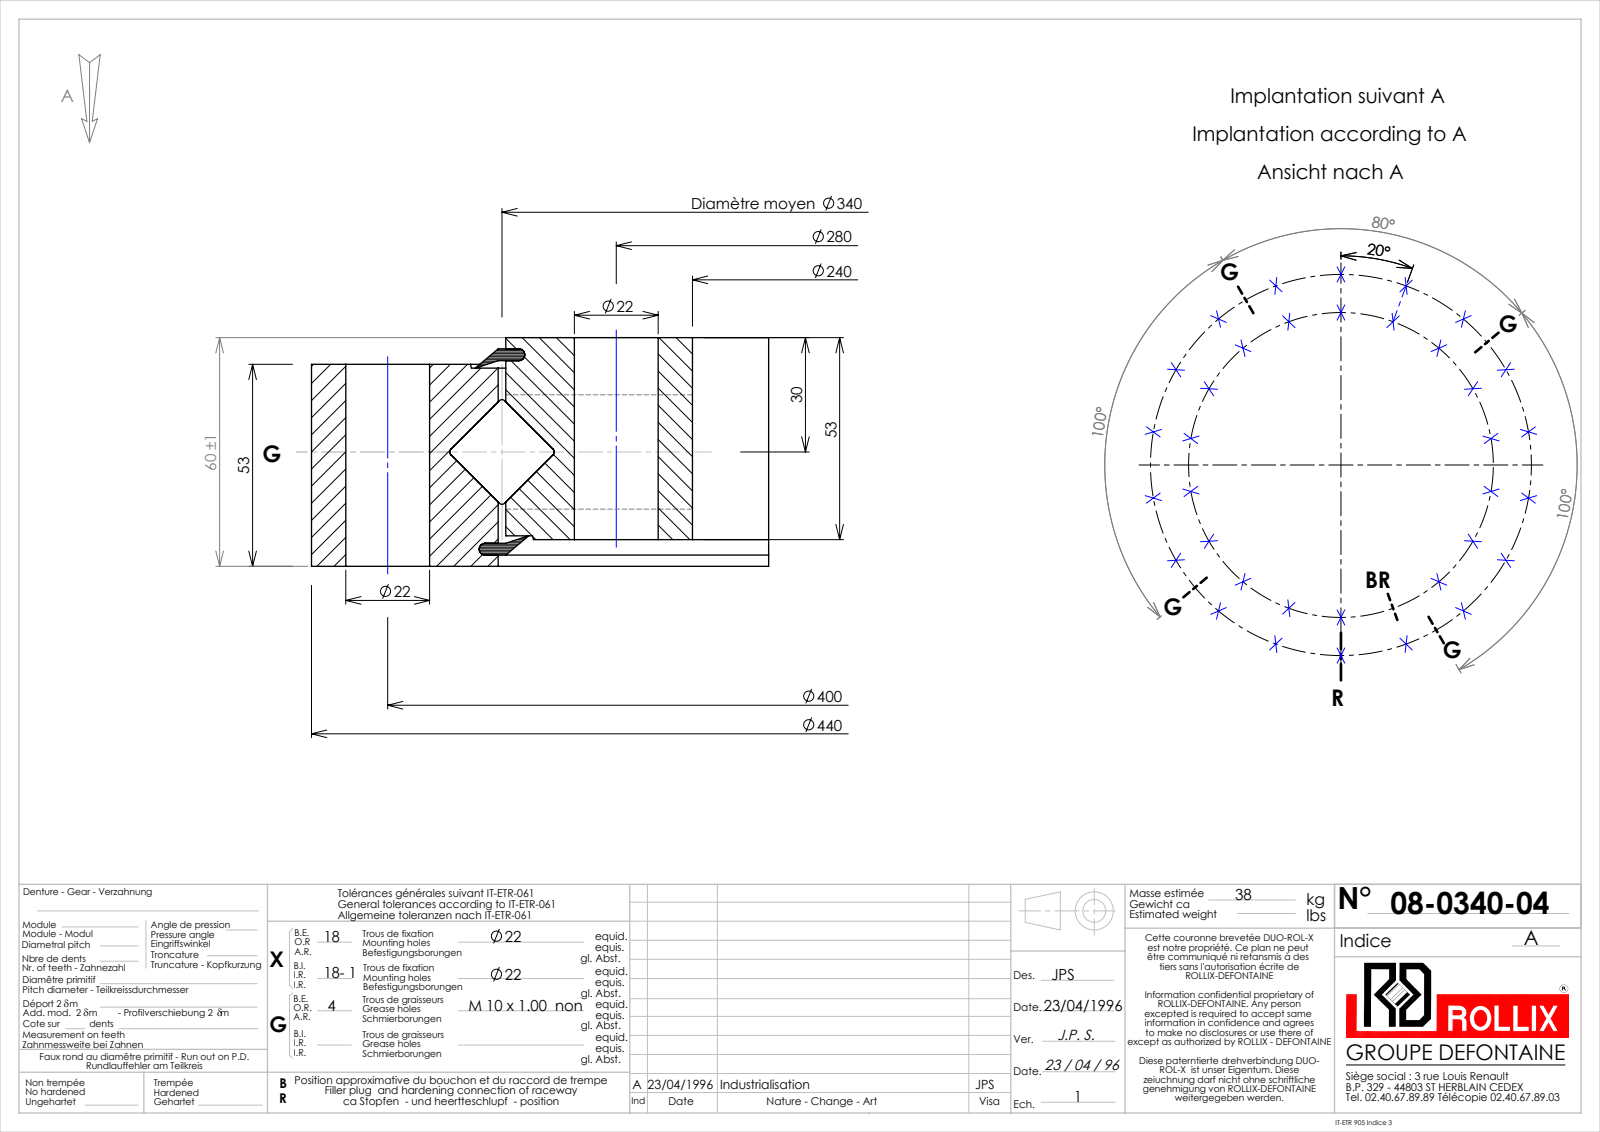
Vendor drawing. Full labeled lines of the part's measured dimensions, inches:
Part name (STEP PRODUCT): 08-0340-04
STEP written by: SolidWorks 2016 (CONFIG_CONTROL_DESIGN)
Units: inches
Bodies: 5 solids, 157 faces (16 planar, 96 cylindrical, 45 other)
Overall size (bounding box): 17.323 × 17.323 × 2.362
Volume: 273.9 in³ · Surface area: 1 003 in²
Round holes (diameter × count): ⌀0.866 ×35, ⌀0.354 ×4, ⌀9.449 ×1, ⌀13.465 ×1
Round bosses / shafts (diameter × count): ⌀17.323 ×1, ⌀13.307 ×1, ⌀0.787 ×1
Main face-to-face distances: 2.087, 0.276, 2.362, 1.811, 0.116, 2.246, 0.159, 1.97, 0.238, 2.124
Hole centre spacings: 7.874, 3.289, 5.512, 8.793, 14.798, 5.088, 13.189, 13.638
